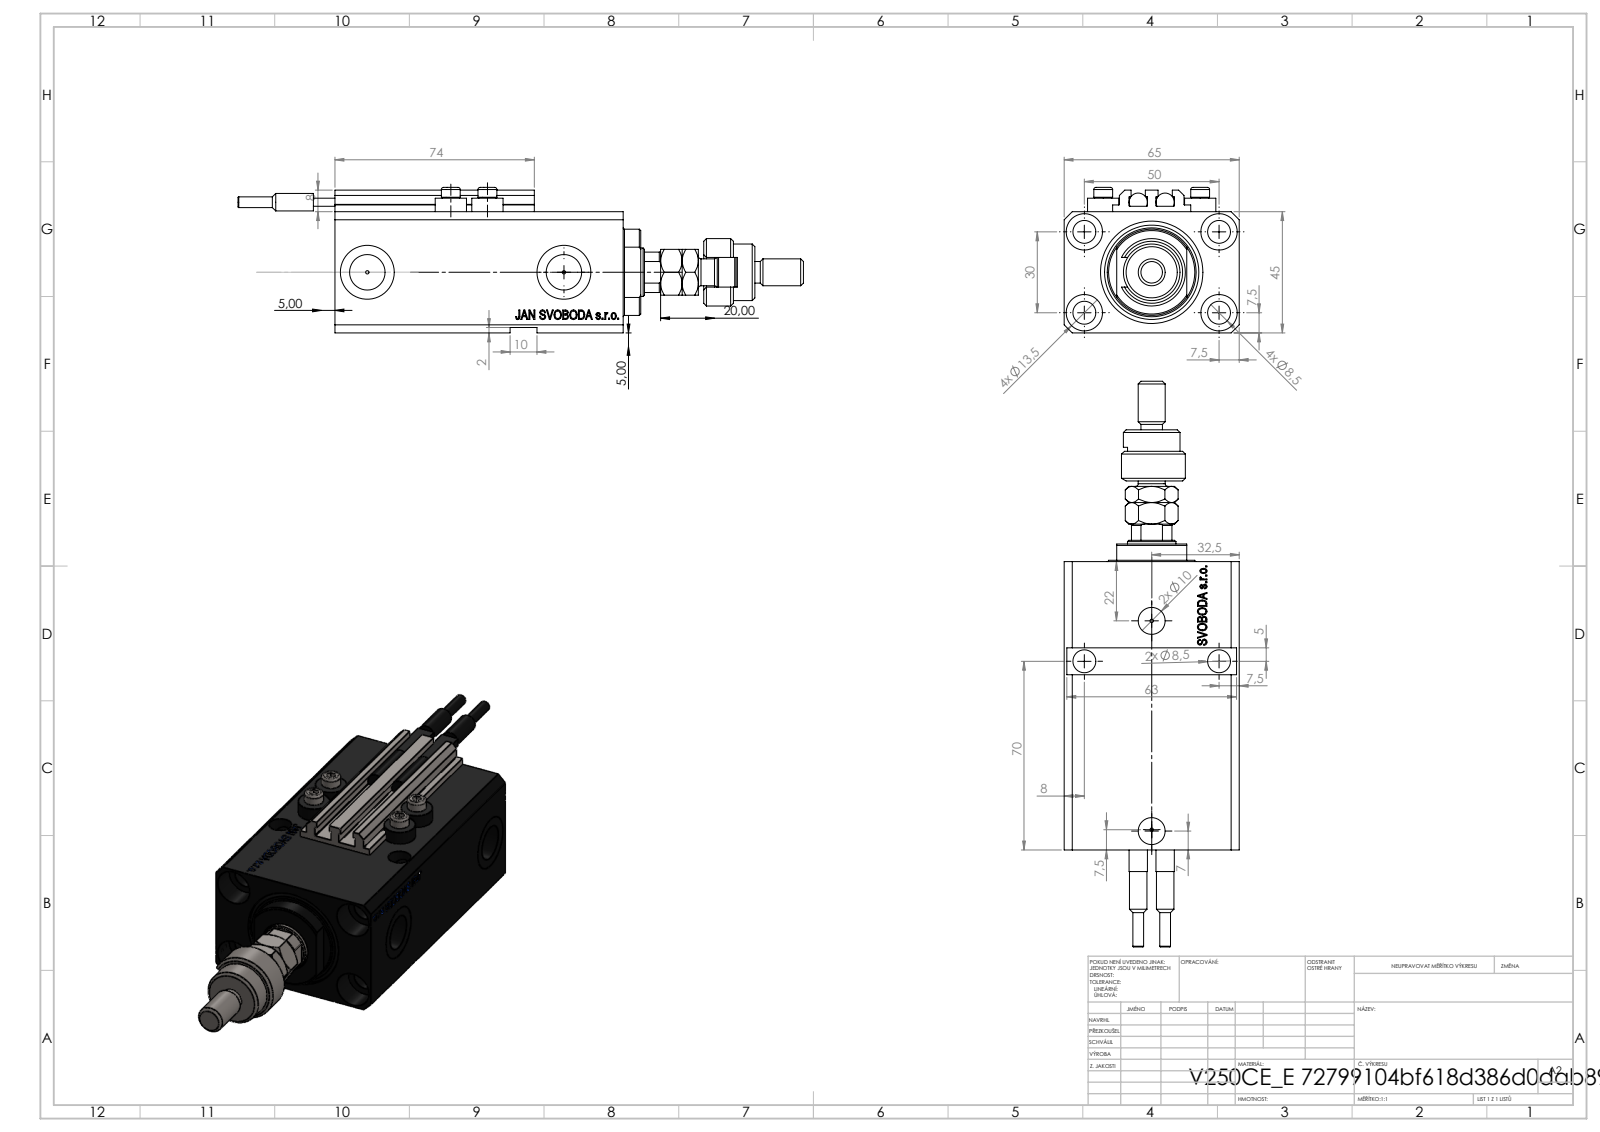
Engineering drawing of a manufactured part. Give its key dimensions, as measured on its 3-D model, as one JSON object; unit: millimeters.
{"part_name": "V250CE_C_VCP; V250CE_VC_E; SWITCH_V250CE; FEMALE_PART_FOR_DFA (+3 more)", "step_written_by": "SolidWorks 2019 (CONFIG_CONTROL_DESIGN)", "units": "millimeters", "bodies": {"solids": 12, "faces": 1240, "planar": 575, "cylindrical": 183, "other": 482}, "overall_size": [210, 65, 54], "volume_mm3": 285151, "surface_area_mm2": 86208, "round_holes": [[8.5, 9], [1.25, 4], [4, 4], [13.5, 4], [10, 2], [13.16, 2], [20, 2], [18, 1], [38, 1]], "round_bosses_or_shafts": [[11.6, 4], [7, 4], [6.8, 2], [6.5, 2], [4, 2], [25, 1], [21, 1], [16, 1]], "partial_cylinders_radius": [[0.2, 10], [5.5, 1], [8.5, 1], [8.75, 1], [16, 1]], "face_to_face_distances": [45, 65, 14, 2, 47, 3, 93, 107, 5, 10], "hole_center_spacings": [29.15, 50, 13.6, 14.76, 15.12, 27.51, 27.89, 30]}
